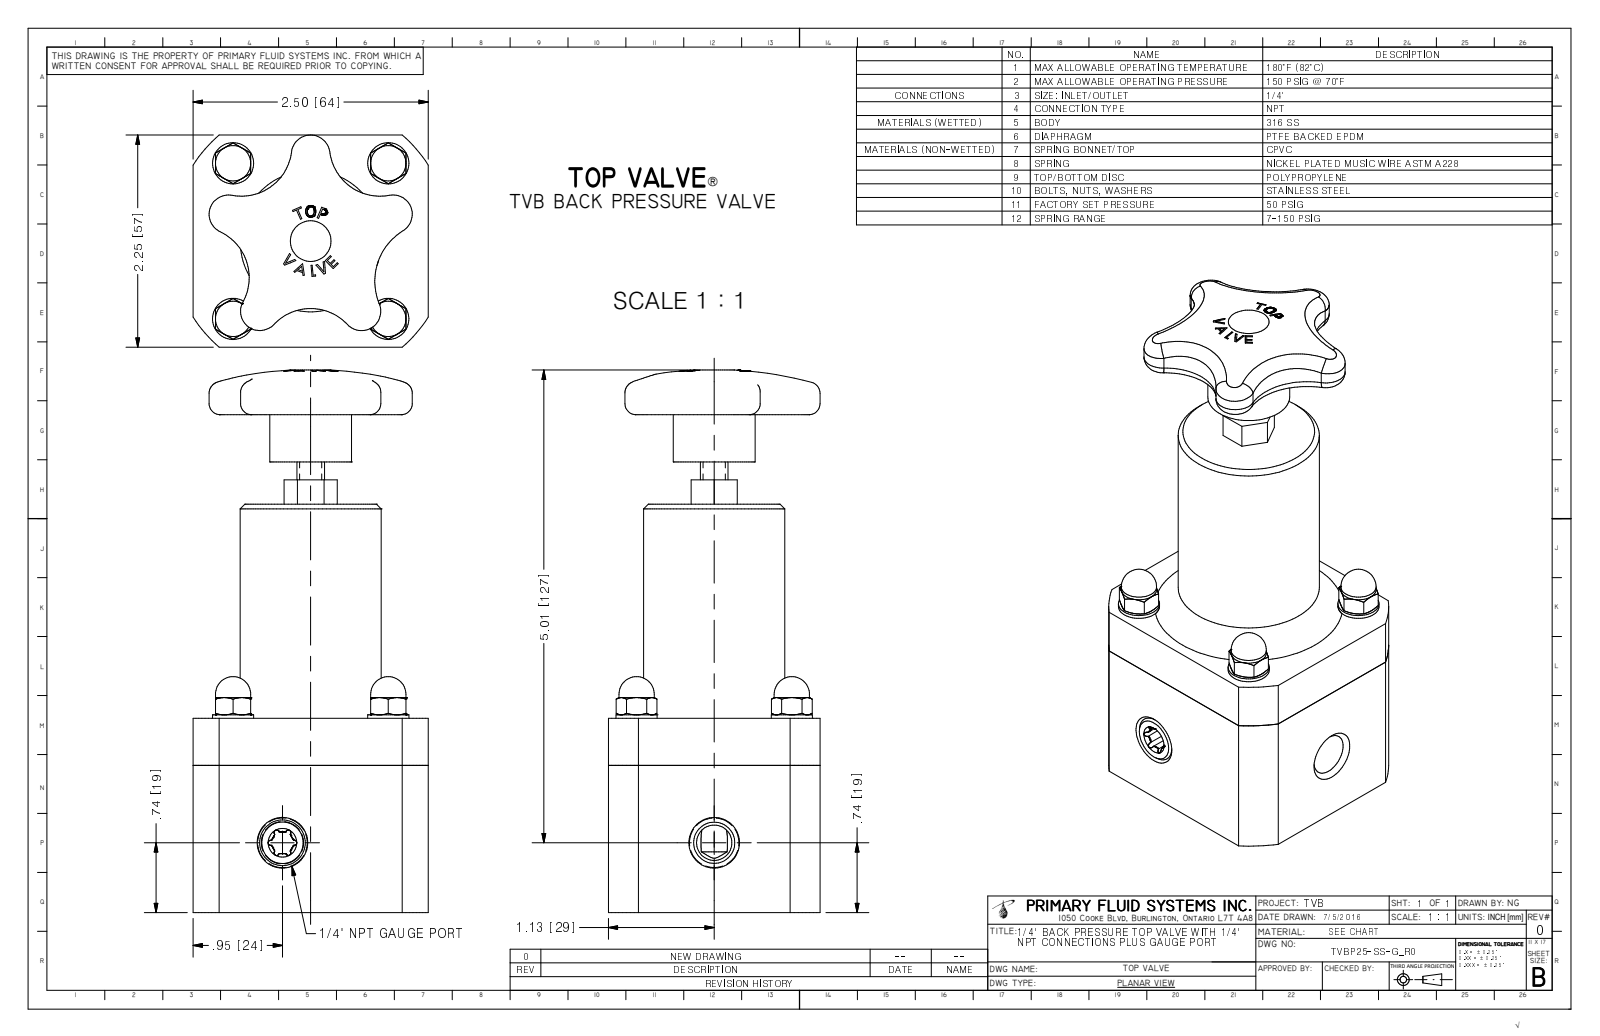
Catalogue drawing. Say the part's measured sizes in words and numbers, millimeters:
The part is named "TVBP25-SS-G-R0". Its 3-D file was written by "Autodesk Inventor 2009 (AUTOMOTIVE_DESIGN)". It is 1 solid with 359 faces: 148 planar, 51 cylindrical and 160 other. Overall it measures 146.1 by 63.5 by 57.2 millimeters. Its volume is 269 700 cubic millimeters and its surface area 35 760 square millimeters. Round holes: 4 of diameter 3.7, 1 of diameter 11.1. Round bosses or shafts: 4 of diameter 11.1, 4 of diameter 9.5, 4 of diameter 7.9, 1 of diameter 38.1, 1 of diameter 22.1, 1 of diameter 7.4. Partial cylindrical surfaces (rounded edges, fillets, slot ends): 6 of radius 0.7, 5 of radius 2.2, 5 of radius 5.2, 4 of radius 13.6, 4 of radius 16.7, 1 of radius 15.9, 1 of radius 18.9, 1 of radius 37.8. The main face-to-face distances are 57.2, 63.5, 52.3, 110, 57.7, 121.4, 69, 11.4, 15.2, 48.3. The hole center spacings are 41.9, 59.3.
